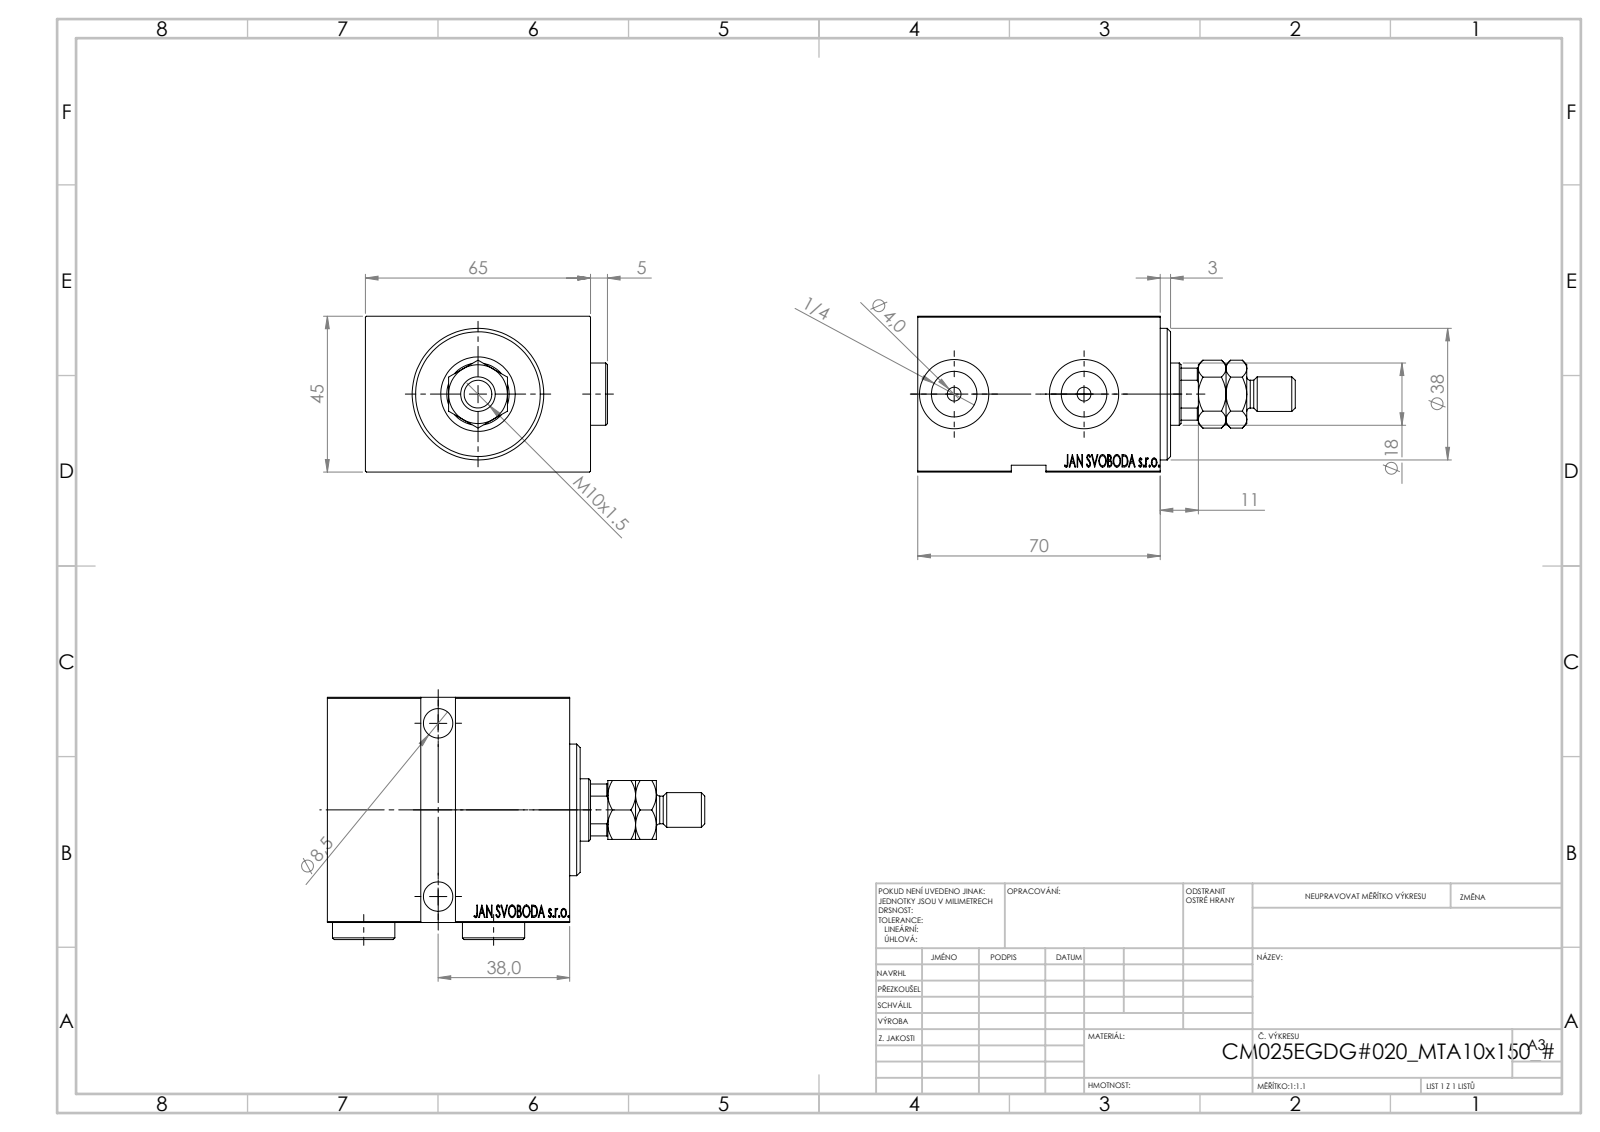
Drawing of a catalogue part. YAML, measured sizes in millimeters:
part_name: "V450CM_VC_B; V450CM_E_VCP; V450CM_E_Body; MTA (+1 more)"
step_written_by: "SolidWorks 2019 (CONFIG_CONTROL_DESIGN)"
units: millimeters
bodies: {solids: 6, faces: 949, planar: 457, cylindrical: 64, other: 428}
overall_size: [109, 69.9, 45]
volume: 194545
surface_area: 44764
round_holes:
  - {diameter: 8.5, count: 3}
  - {diameter: 4, count: 2}
  - {diameter: 13.16, count: 2}
  - {diameter: 13.5, count: 2}
  - {diameter: 20, count: 2}
  - {diameter: 18, count: 1}
  - {diameter: 21.5, count: 1}
  - {diameter: 25, count: 1}
  - {diameter: 35, count: 1}
round_bosses_or_shafts:
  - {diameter: 18, count: 2}
  - {diameter: 38, count: 1}
  - {diameter: 27, count: 1}
  - {diameter: 10, count: 1}
  - {diameter: 8, count: 1}
partial_cylinders:
  - {radius: 8.5, count: 1}
face_to_face_distances: [45, 65, 70, 8, 5, 64.9, 3, 6, 64, 59]
hole_center_spacings: [37.5, 50]
